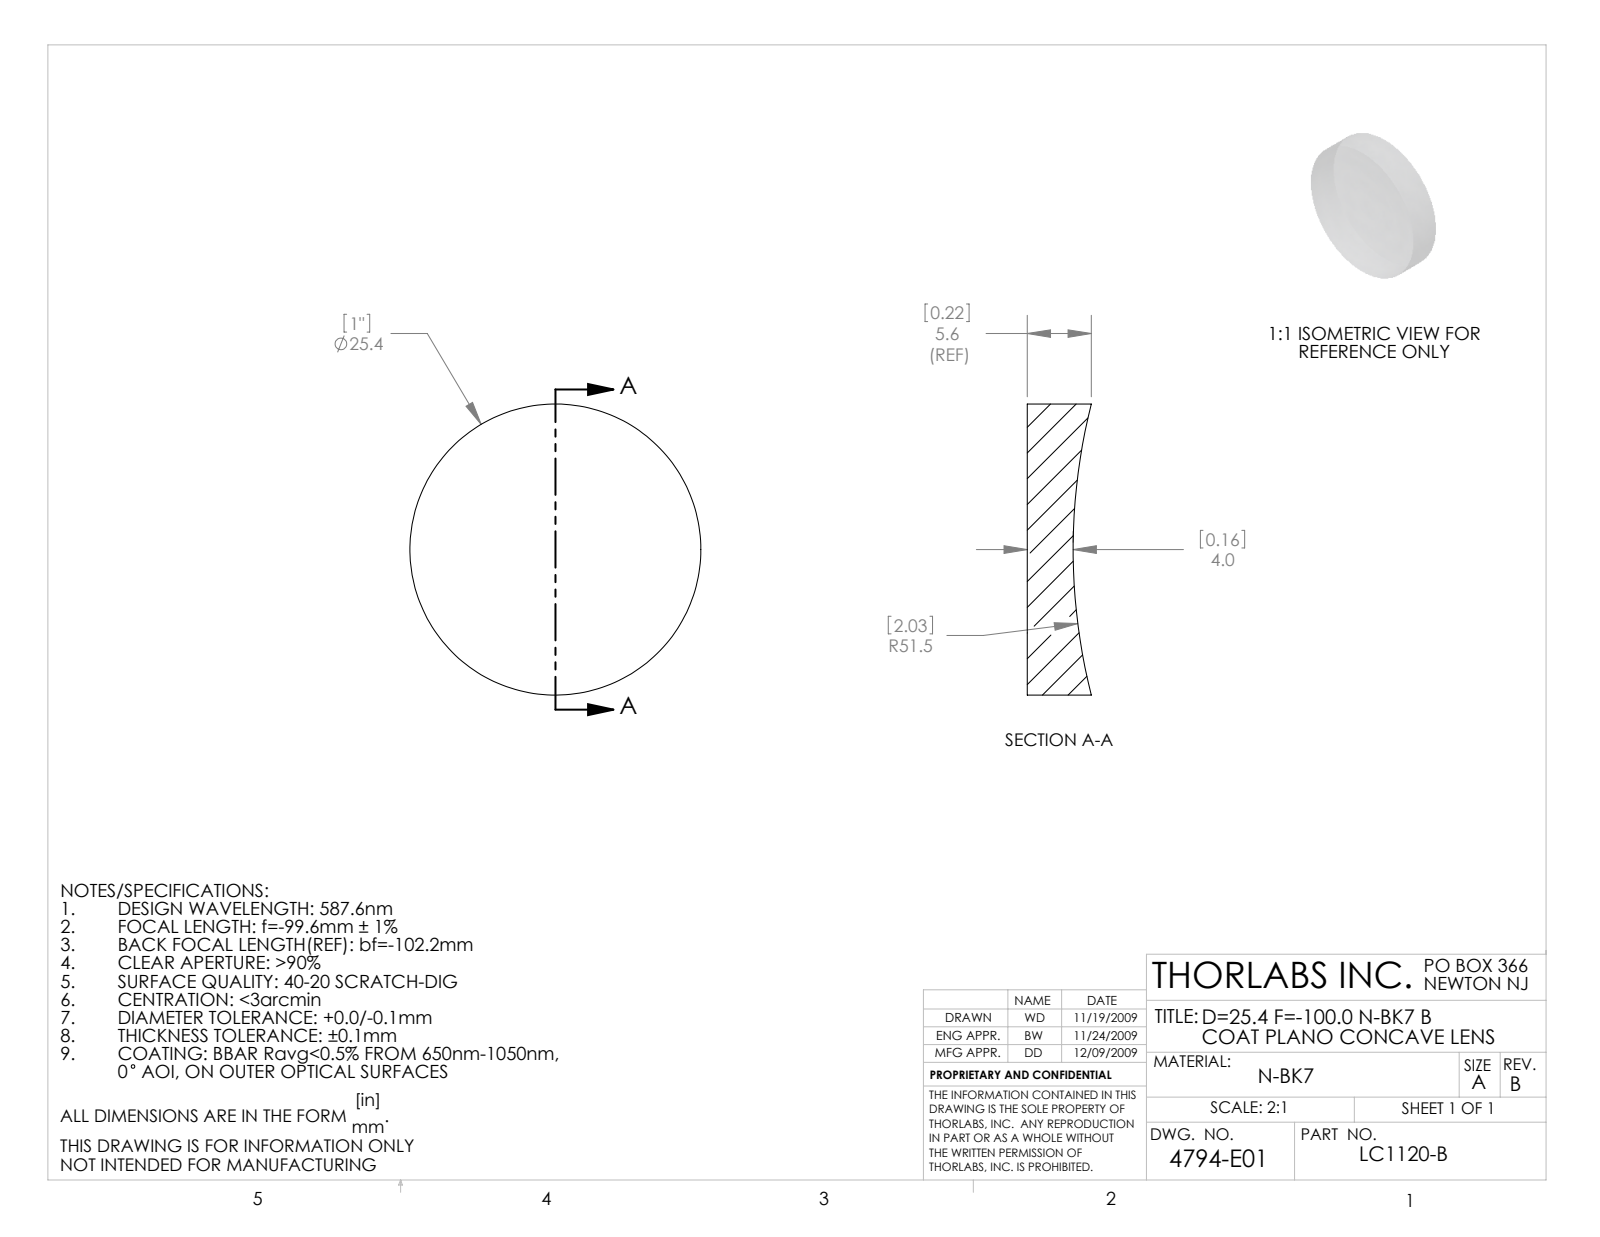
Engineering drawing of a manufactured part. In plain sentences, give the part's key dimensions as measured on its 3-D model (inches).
The part is named "4794-E0W". Its 3-D file was written by "SolidWorks 2009 (AUTOMOTIVE_DESIGN)". It is 1 solid with 5 faces: 1 planar, 2 cylindrical and 2 other. Overall it measures 1 by 1 by 0.22 inches. Its volume is 0.148 cubic inches and its surface area 2.275 square inches. Round bosses or shafts: 1 of diameter 1.
